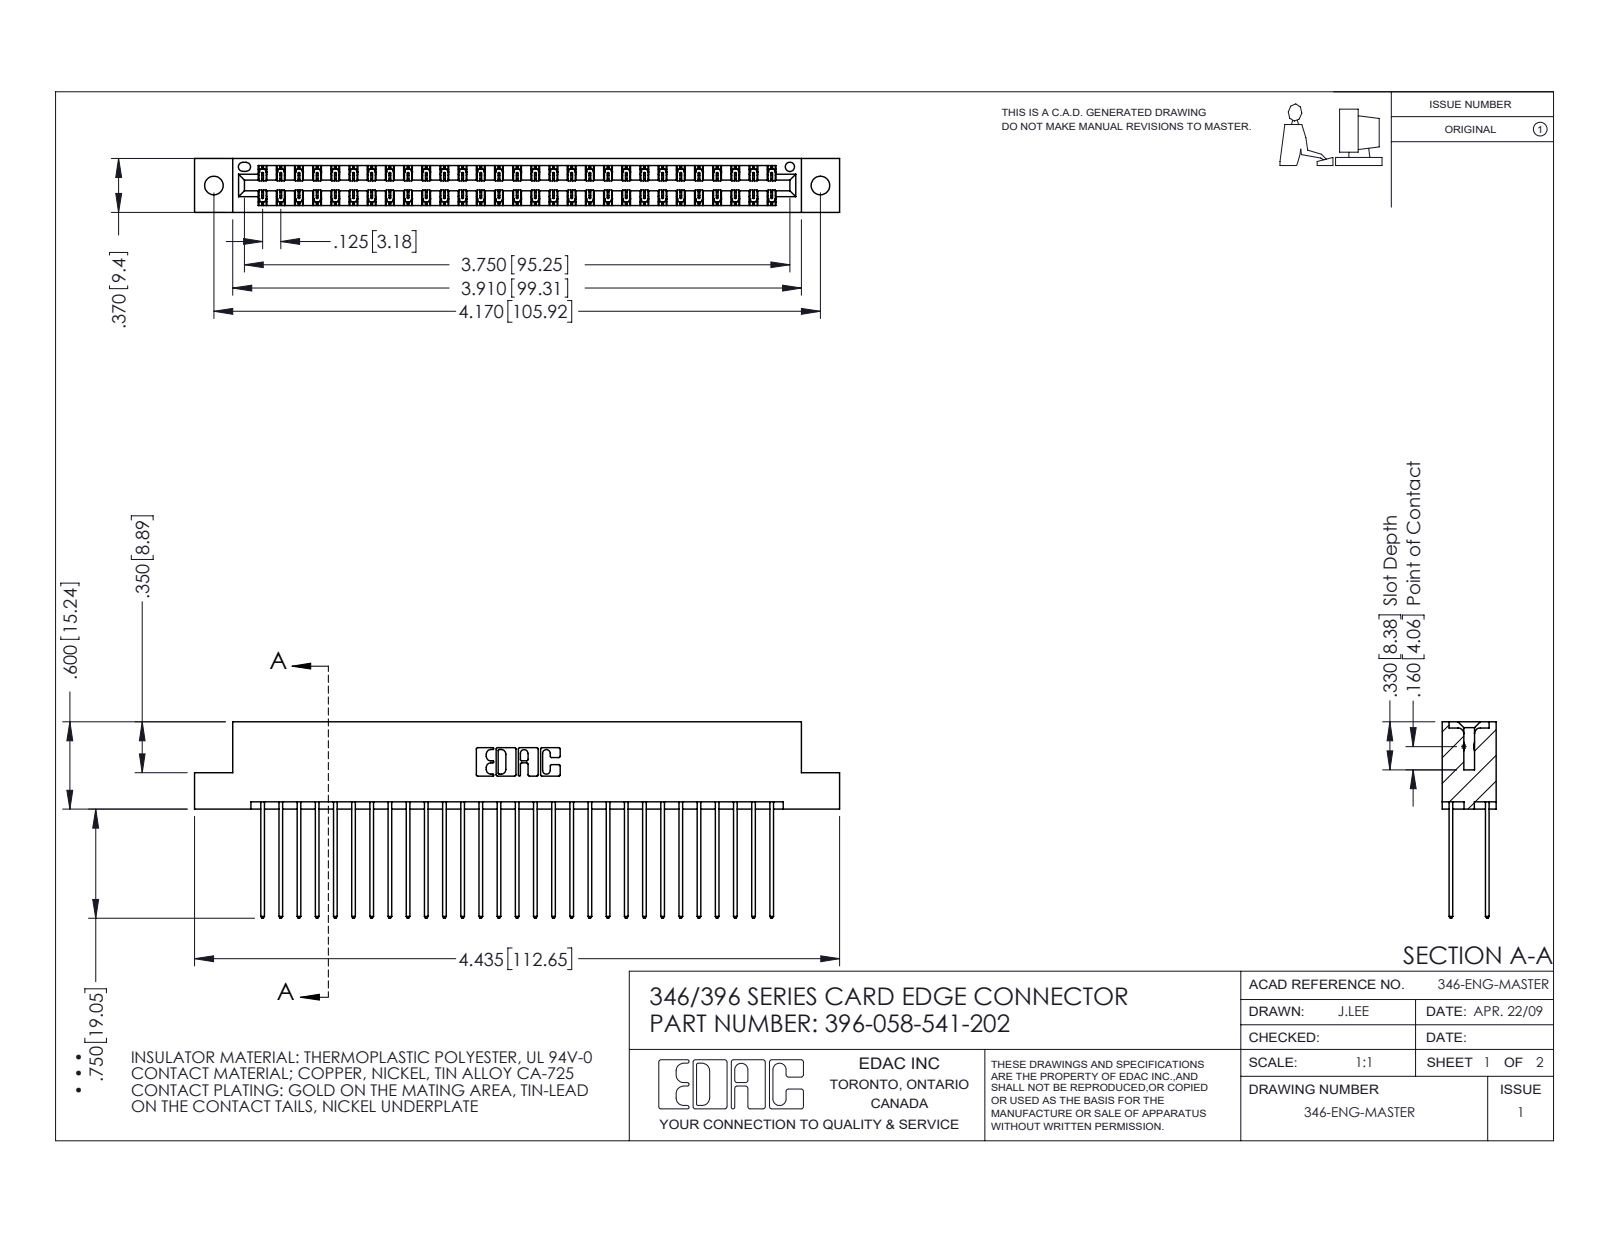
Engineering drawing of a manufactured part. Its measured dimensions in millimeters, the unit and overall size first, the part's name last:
Units: millimetres
Overall size (bounding box): 112.6 × 34.3 × 9.4
Round holes (diameter × count): ⌀3.3 ×2, ⌀1.6 ×1
Partial cylindrical surfaces — rounded edges, fillets, slot ends (radius × count): R0.2 ×87, R0.3 ×58, R0.3 ×22, R0.2 ×6, R0.8 ×6, R0.7 ×3, R0.4 ×2, R0.6 ×2
Main face-to-face distances: 1.2, 8.2, 6.4, 1.8, 7.6, 0.6, 9.4, 7, 5.7, 3.8
Hole centre spacings: 6.2, 100.6, 105.9
Volume: 11 200 mm³ · Surface area: 16 490 mm²
Bodies: 59 solids, 3138 faces (2106 planar, 1032 cylindrical, 0 other)
Part name (STEP PRODUCT): 346 Part_Flush Mounting Lugs - 0.128 Dia; 396-058-541-202; 345-292-001_345-293-141
STEP written by: SolidWorks 2016 (CONFIG_CONTROL_DESIGN)
